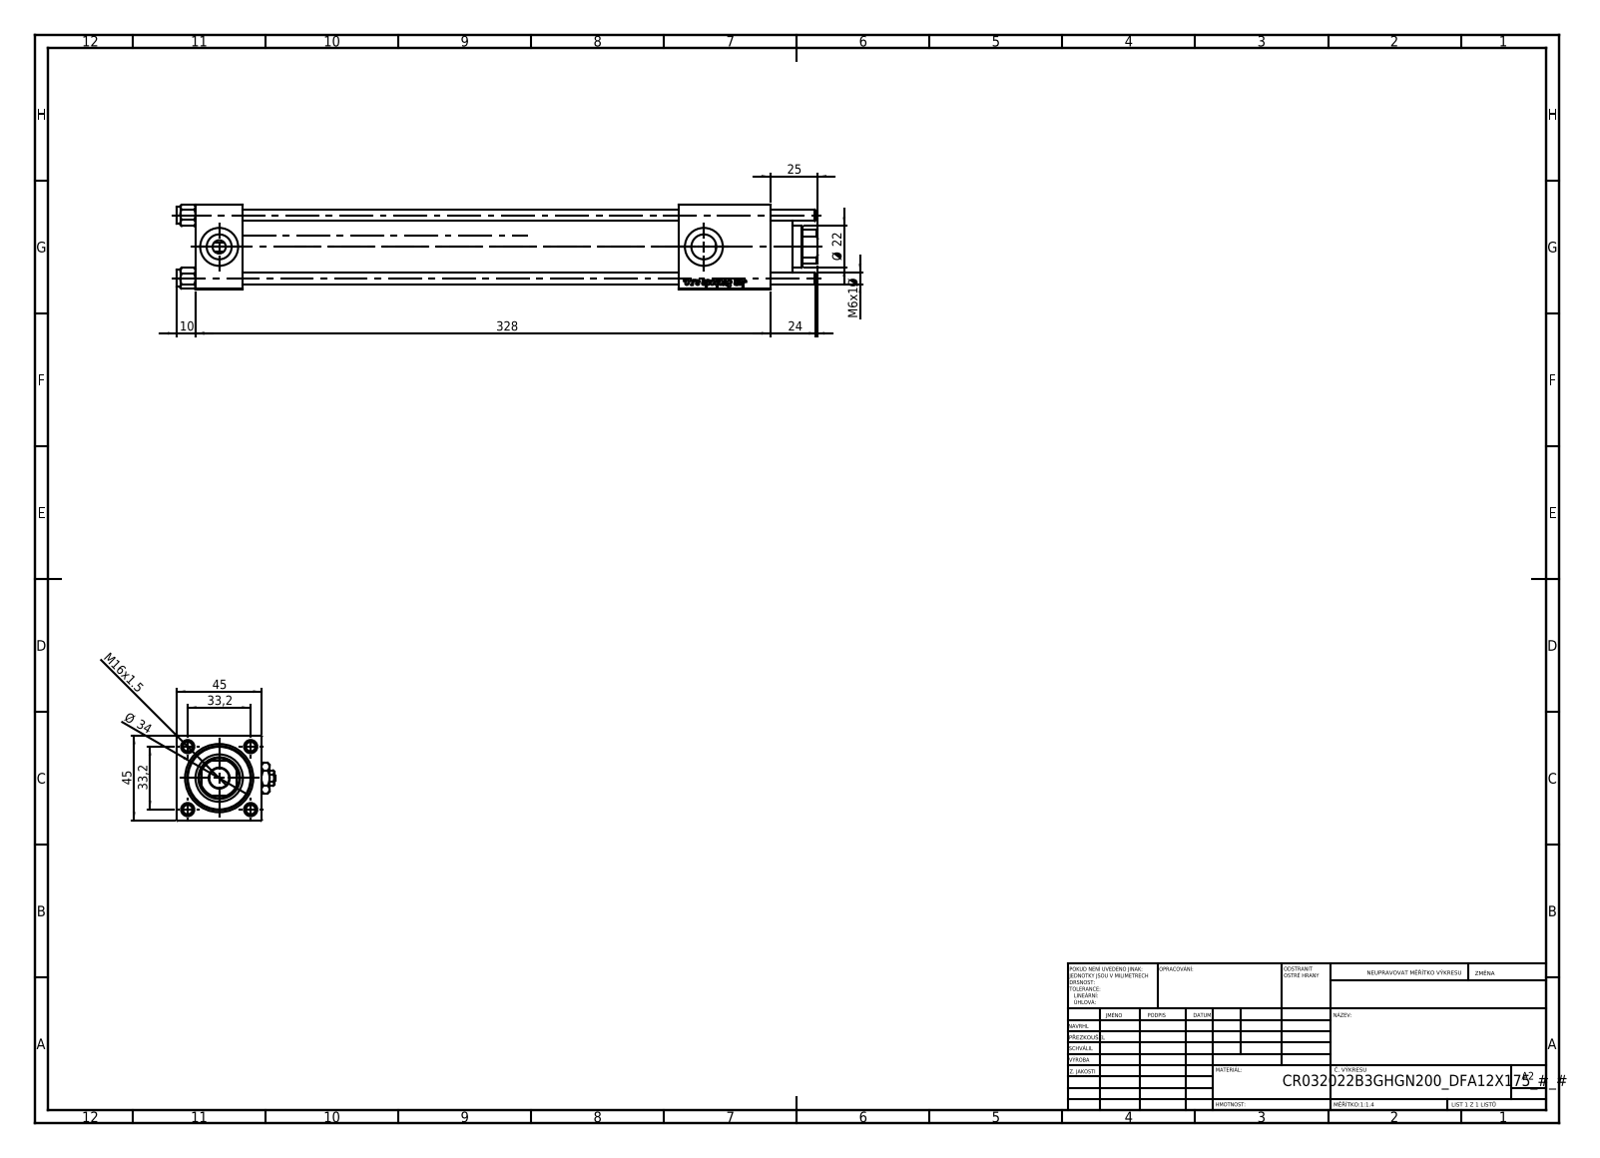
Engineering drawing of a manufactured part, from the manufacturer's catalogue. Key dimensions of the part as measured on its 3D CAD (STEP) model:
Part name (STEP PRODUCT): FEMALE_PART_FOR_DFA; V215CR_B-1; V215_VC_A; V215CR_B_TYCINKA (+3 more)
STEP written by: SolidWorks 2019 (CONFIG_CONTROL_DESIGN)
Units: millimetres
Bodies: 14 solids, 1289 faces (490 planar, 97 cylindrical, 702 other)
Overall size (bounding box): 338 × 52 × 45
Volume: 370 750 mm³ · Surface area: 148 650 mm²
Round holes (diameter × count): ⌀6 ×4, ⌀7 ×2, ⌀13.16 ×2, ⌀20 ×2, ⌀10.5 ×1, ⌀22 ×1, ⌀24 ×1, ⌀25 ×1, ⌀32 ×1, ⌀33 ×1
Round bosses / shafts (diameter × count): ⌀9 ×4, ⌀38 ×1, ⌀34 ×1, ⌀28 ×1, ⌀12 ×1, ⌀10 ×1
Partial cylindrical surfaces — rounded edges, fillets, slot ends (radius × count): R9.75 ×1, R10.5 ×1
Main face-to-face distances: 45, 25, 303, 255, 230, 44.8, 278, 48, 274.3, 249.3
Hole centre spacings: 23.48, 33.2, 46.95, 255.5
